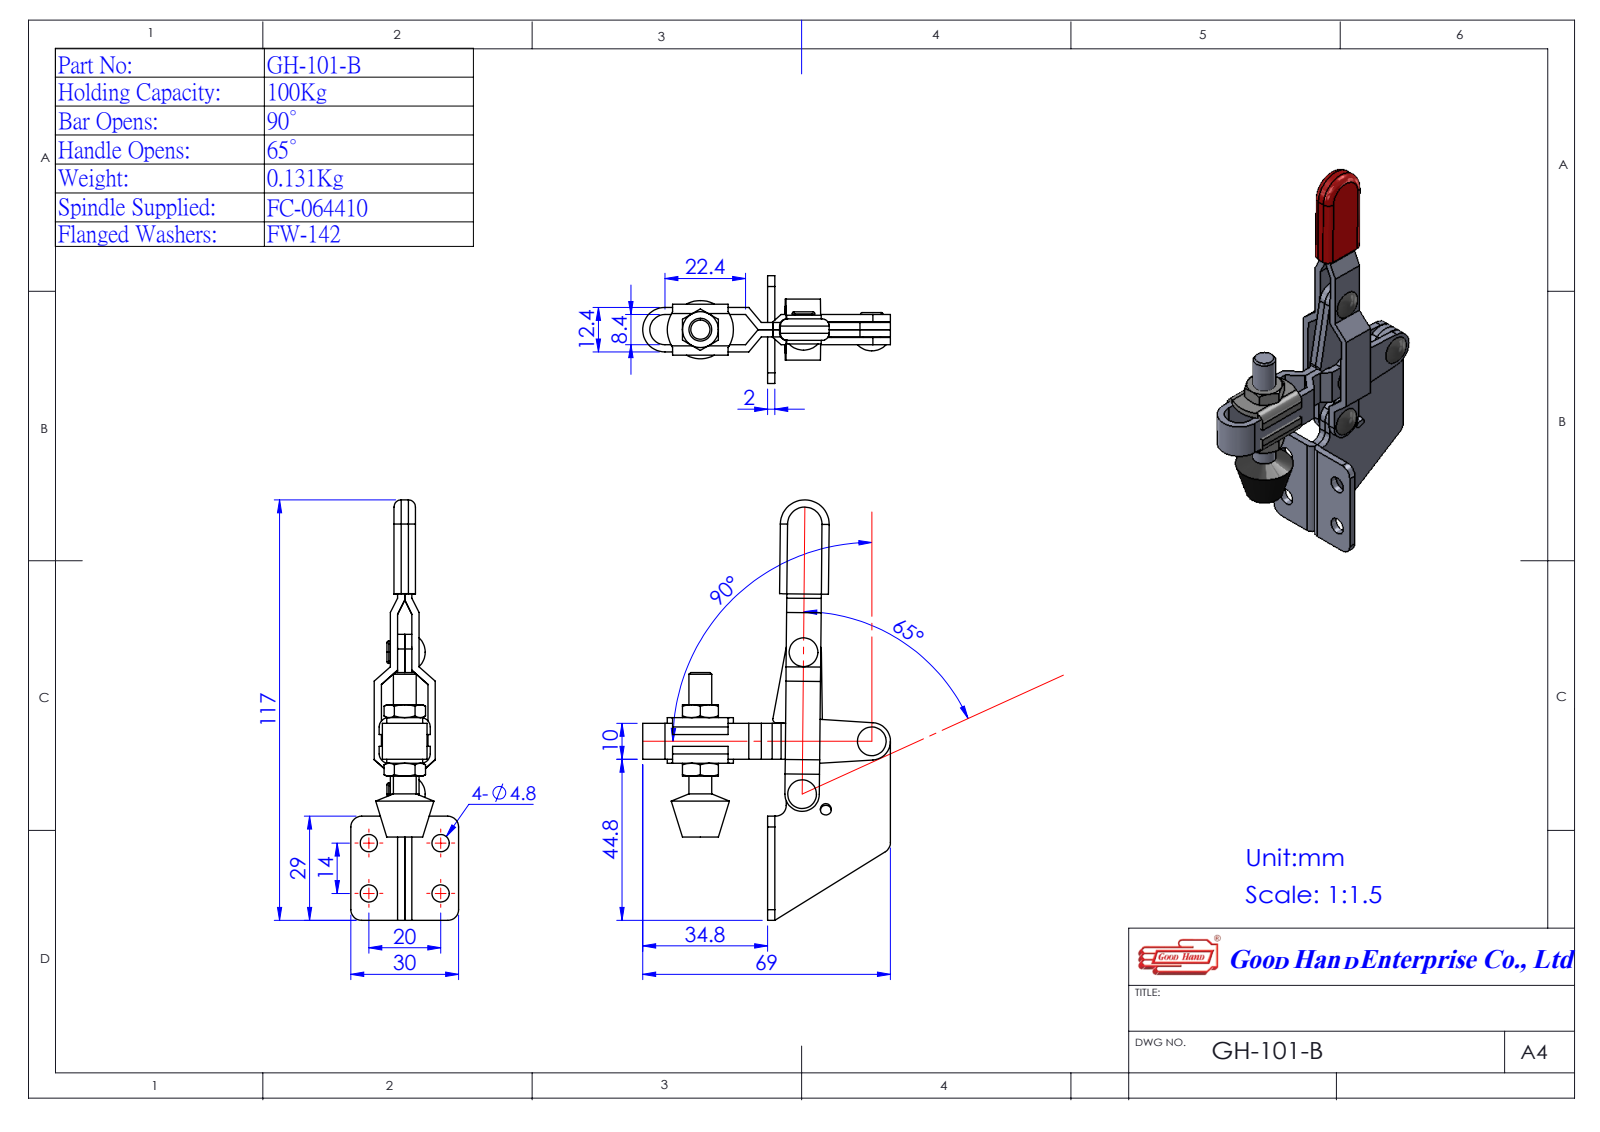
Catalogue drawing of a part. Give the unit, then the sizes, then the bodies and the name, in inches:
Units: inches
Overall size (bounding box): 4.607 × 2.717 × 1.181
Round holes (diameter × count): ⌀0.118 ×4, ⌀0.189 ×4, ⌀0.191 ×2
Round bosses / shafts (diameter × count): ⌀0.189 ×2, ⌀0.25 ×1
Partial cylindrical surfaces — rounded edges, fillets, slot ends (radius × count): R0.118 ×6, R0.039 ×4, R0.102 ×4, R0.197 ×2, R0.165 ×1, R0.173 ×1, R0.189 ×1, R0.205 ×1
Main face-to-face distances: 0.079, 0.157, 0.087, 0.244, 0.165, 0.039, 0.331, 0.5, 0.091, 0.169
Hole centre spacings: 0.551, 0.787, 0.961, 0.58, 0.736, 0.958, 0.976, 1.23
Volume: 1.184 in³ · Surface area: 25.74 in²
Bodies: 5 solids, 286 faces (149 planar, 87 cylindrical, 50 other)
Part name (STEP PRODUCT): Group2^GH-101-B; Group4^GH-101-B; Group5^GH-101-B; Group1^GH-101-B (+2 more)
STEP written by: SolidWorks 2016 (AUTOMOTIVE_DESIGN)
